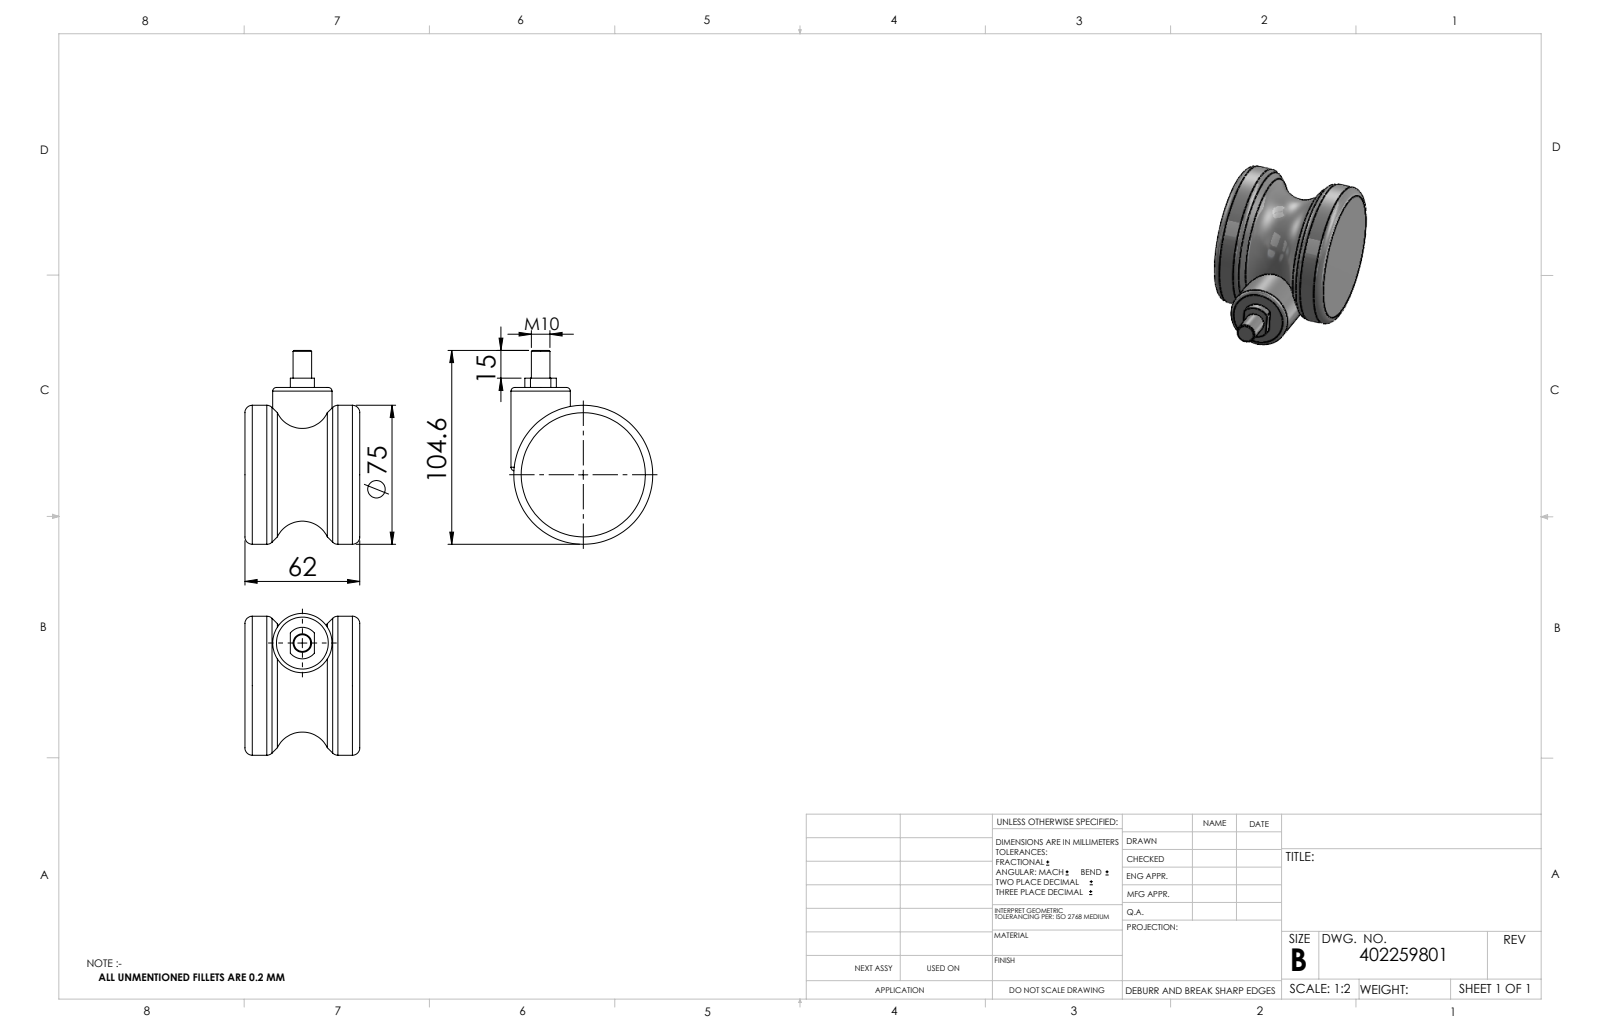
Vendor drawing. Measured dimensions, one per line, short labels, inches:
name: 402259801_c_1
written by: SolidWorks 2014 (CONFIG_CONTROL_DESIGN)
unit: in
bodies: 1 solid, 37 faces (8 planar, 10 cylindrical, 19 other)
size: 4.118 × 3.012 × 2.441
volume: 14.77 in³; area: 40.46 in²
bosses: 1× ⌀2.953, 1× ⌀1.26, 1× ⌀0.394
rounds: 1× R0.335
face distances: 2.441, 1.772, 1.969, 0.197, 0.965, 1.476, 2.559, 0.787, 0.591, 0.512
